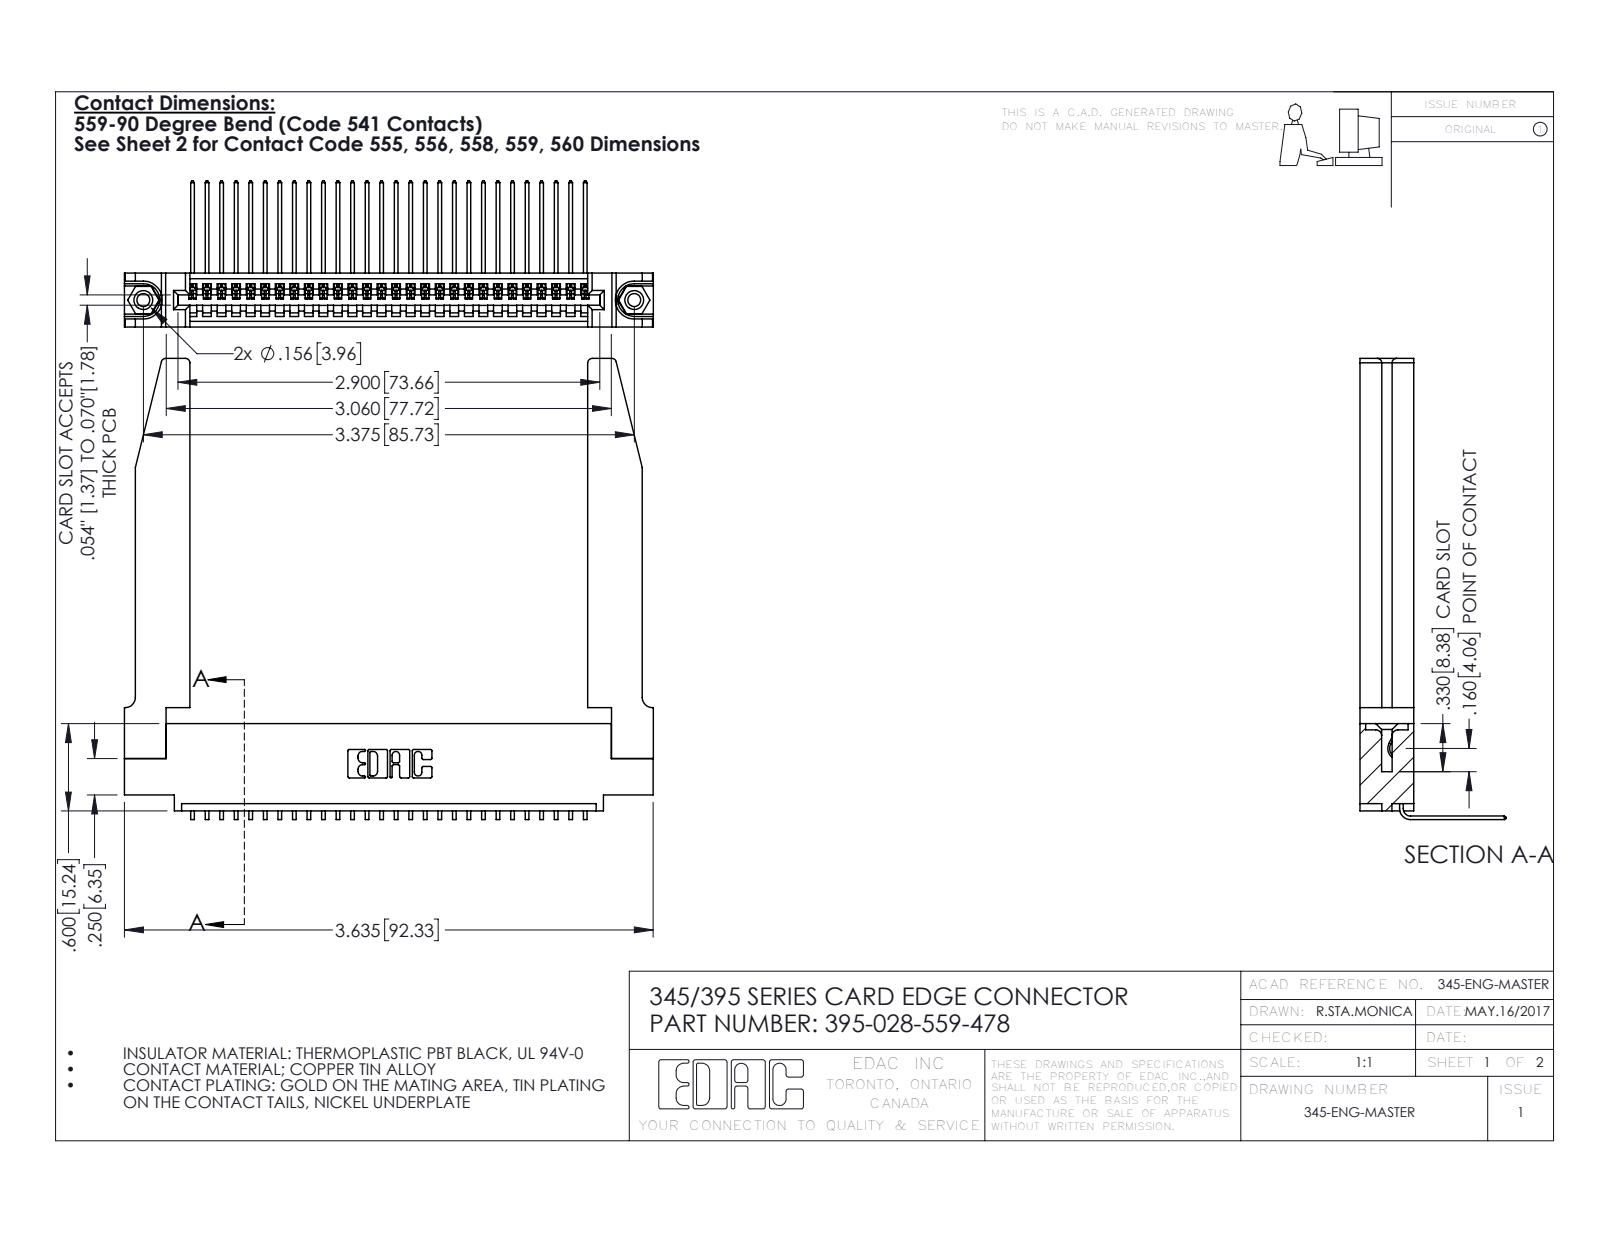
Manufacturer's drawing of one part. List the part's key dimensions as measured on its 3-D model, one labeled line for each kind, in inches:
Part name (STEP PRODUCT): 345-292-001_558 559 Tail - 1; 345 Part_0.110 Offset - 0.156 Dia-TH; 395-028-559-478; 345-250-001_345-250-001-102 (+1 more)
STEP written by: SolidWorks 2016 (CONFIG_CONTROL_DESIGN)
Units: inches
Bodies: 33 solids, 2044 faces (1402 planar, 590 cylindrical, 52 other)
Overall size (bounding box): 3.636 × 3.169 × 1.005
Volume: 1.004 in³ · Surface area: 29.17 in²
Round holes (diameter × count): ⌀0.089 ×2, ⌀0.125 ×2, ⌀0.156 ×2, ⌀0.064 ×1
Round bosses / shafts (diameter × count): ⌀0.155 ×2
Partial cylindrical surfaces — rounded edges, fillets, slot ends (radius × count): R0.006 ×56, R0.01 ×22, R0.03 ×8, R0.007 ×6, R0.031 ×6, R0.026 ×3, R0.031 ×2, R0.04 ×2
Main face-to-face distances: 0.37, 0.072, 0.298, 0.098, 0.272, 0.025, 0.2, 0.148, 0.15, 0.225
Hole centre spacings: 0.27, 3.14, 3.375
